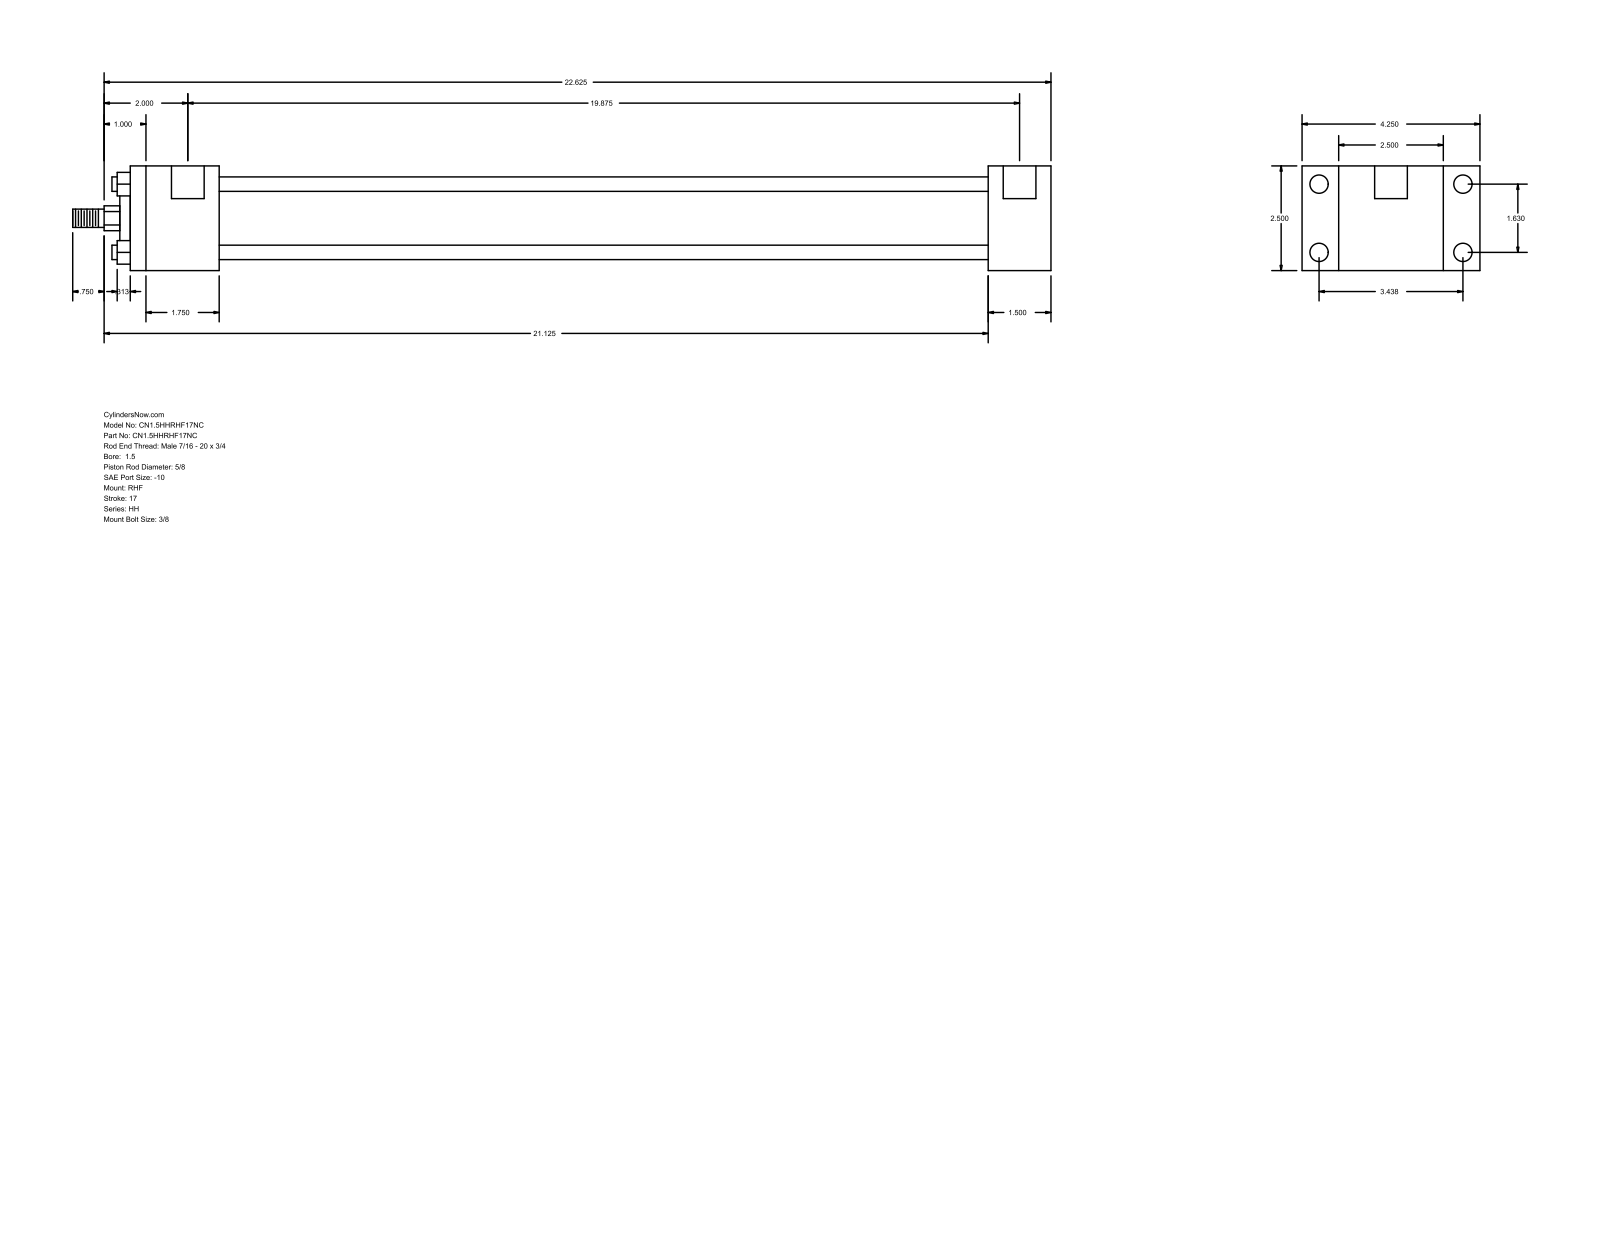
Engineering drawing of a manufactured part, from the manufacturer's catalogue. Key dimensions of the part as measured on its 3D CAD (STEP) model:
Part name (STEP PRODUCT): HH_RHF__0150_0.625
STEP written by: GSSL Pune (CONFIG_CONTROL_DESIGN)
Units: millimetres
Bodies: 0 solids, 88 faces (60 planar, 28 cylindrical, 0 other)
Overall size (bounding box): 593.73 × 107.95 × 63.5
Round holes (diameter × count): ⌀5.56 ×4, ⌀11.13 ×4, ⌀19.84 ×2
Round bosses / shafts (diameter × count): ⌀8.76 ×4, ⌀44.45 ×1, ⌀28.57 ×1, ⌀15.88 ×1, ⌀11.11 ×1
Partial cylindrical surfaces — rounded edges, fillets, slot ends (radius × count): R7.54 ×1
Main face-to-face distances: 63.5, 22.23, 85.73, 38.09, 520.7, 558.79, 107.96, 53.97, 466.73, 504.82
Hole centre spacings: 1.59, 41.4, 87.32, 96.64, 506.41, 508, 504.82
